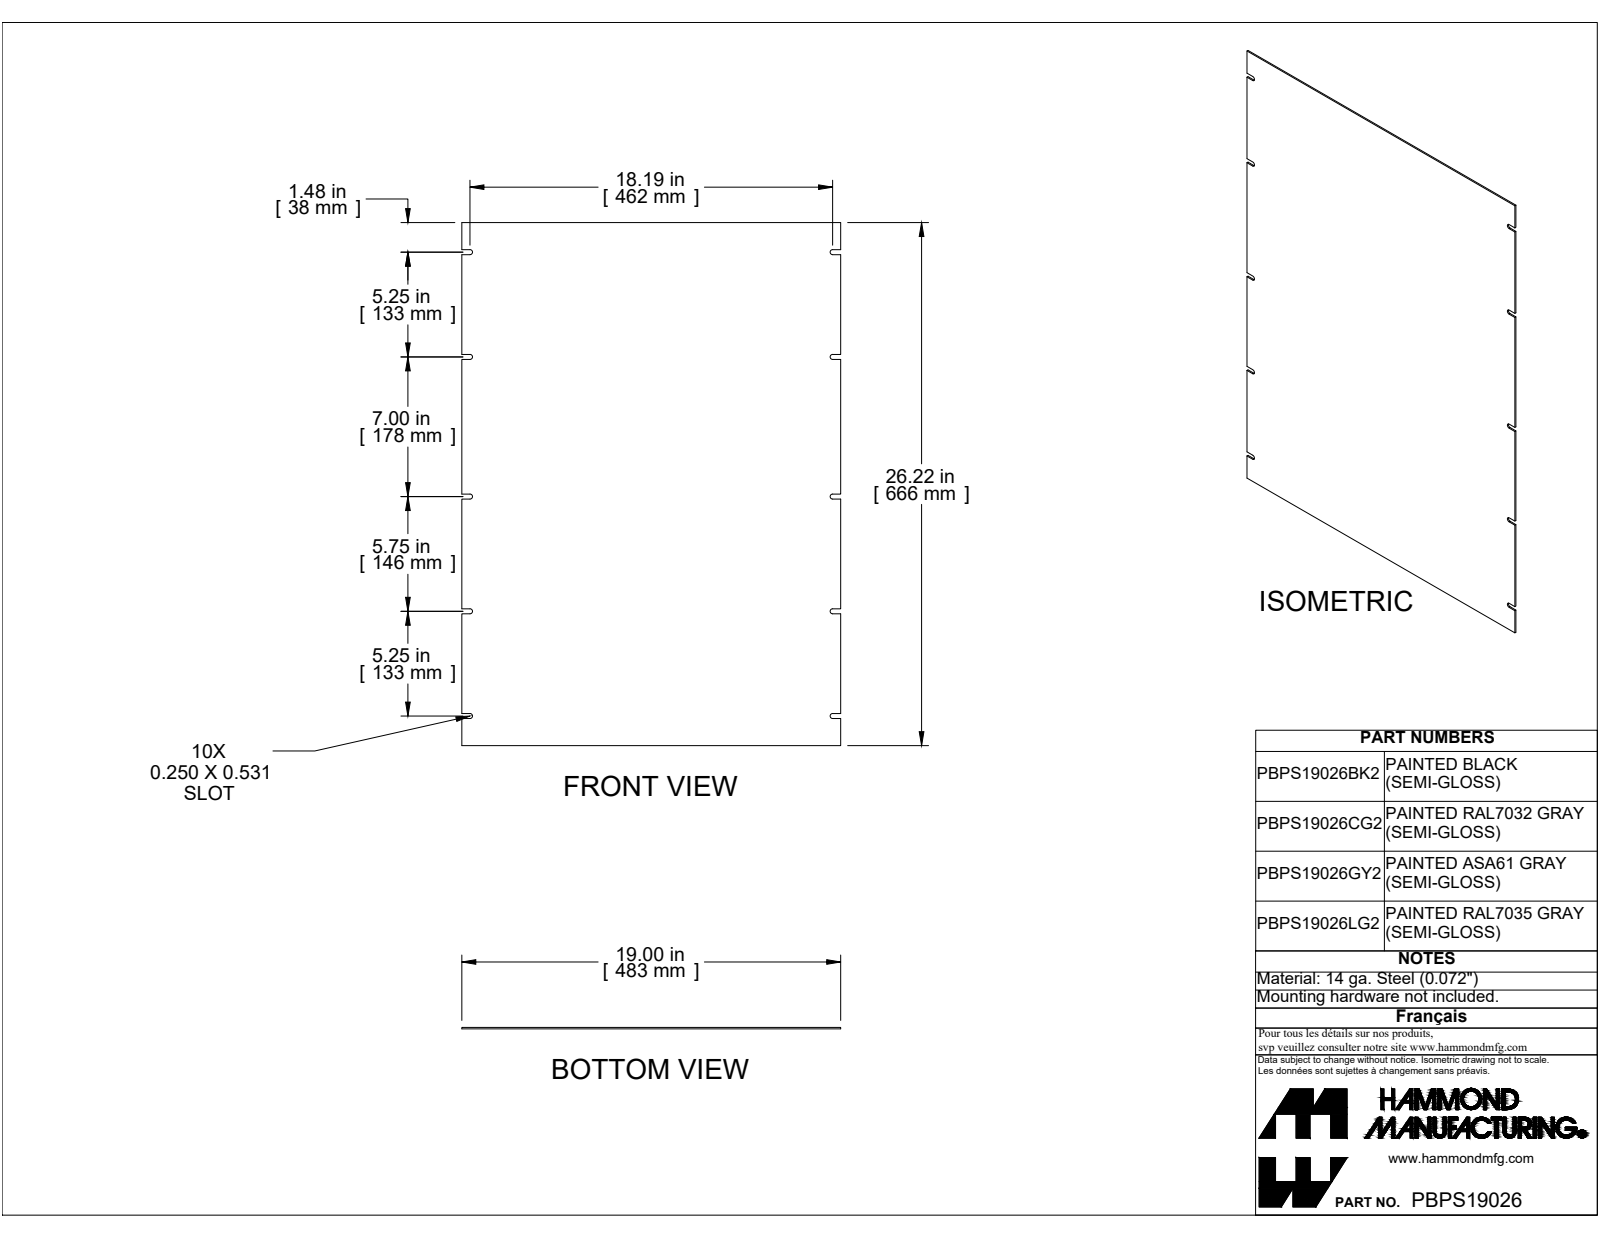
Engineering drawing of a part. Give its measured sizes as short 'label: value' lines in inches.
name: PBPS19026LG2
written by: SolidWorks 2019 (CONFIG_CONTROL_DESIGN)
unit: in
bodies: 1 solid, 46 faces (36 planar, 10 cylindrical, 0 other)
size: 26.218 × 19 × 0.072
volume: 35.78 in³; area: 1 001 in²
rounds: 10× R0.125
face distances: 0.072, 19, 26.218, 5.25, 0.25, 18, 12.75, 5.5, 5, 6.609
